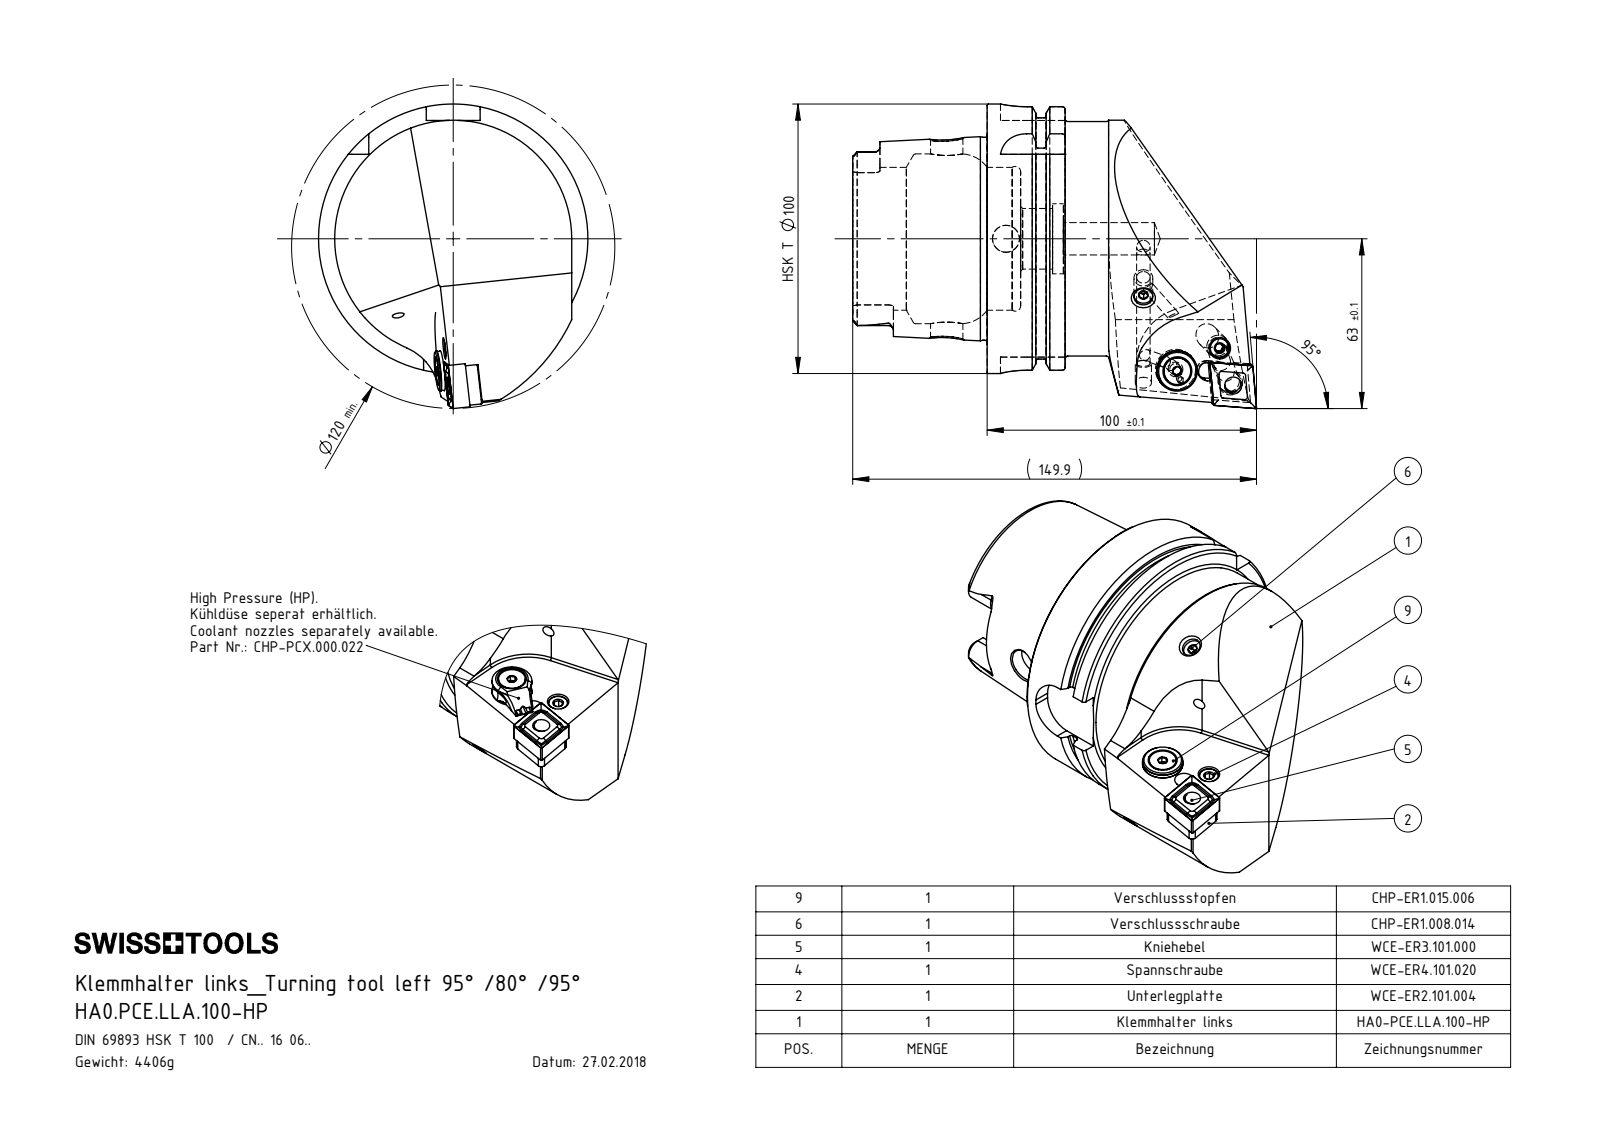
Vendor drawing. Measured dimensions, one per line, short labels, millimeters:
name: HA0.PCE.LLA.100-HP; DIN 7991 - M5x15; WCE-ER3.101.000_A; CHP-ER1.015.006_A (+8 more)
written by: SolidWorks 2017 (AUTOMOTIVE_DESIGN)
unit: mm
bodies: 13 solids, 516 faces (158 planar, 144 cylindrical, 214 other)
size: 149.9 × 113 × 100
volume: 560 336 mm³; area: 76 181 mm²
holes: 4× ⌀5, 2× ⌀4.2, 2× ⌀7, 2× ⌀12, 1× ⌀1.2, 1× ⌀2, 1× ⌀2.5, 1× ⌀3, 1× ⌀5.2, 1× ⌀6, 1× ⌀6.35, 1× ⌀8.05
bosses: 2× ⌀8, 2× ⌀6, 1× ⌀100, 1× ⌀91.95, 1× ⌀87, 1× ⌀75.26, 1× ⌀15, 1× ⌀13.4
rounds: 6× R1.9, 4× R0.4, 4× R1.5, 4× R10, 3× R3.5, 2× R0.3, 2× R0.8, 2× R4.83
face distances: 12.45, 28.95, 16.5, 49.9, 62.35, 78.85, 87.8, 78.2, 28.3, 15.85
hole spacings: 4.51, 18.72, 19.37, 22, 4.49, 4.5, 14.75, 15
